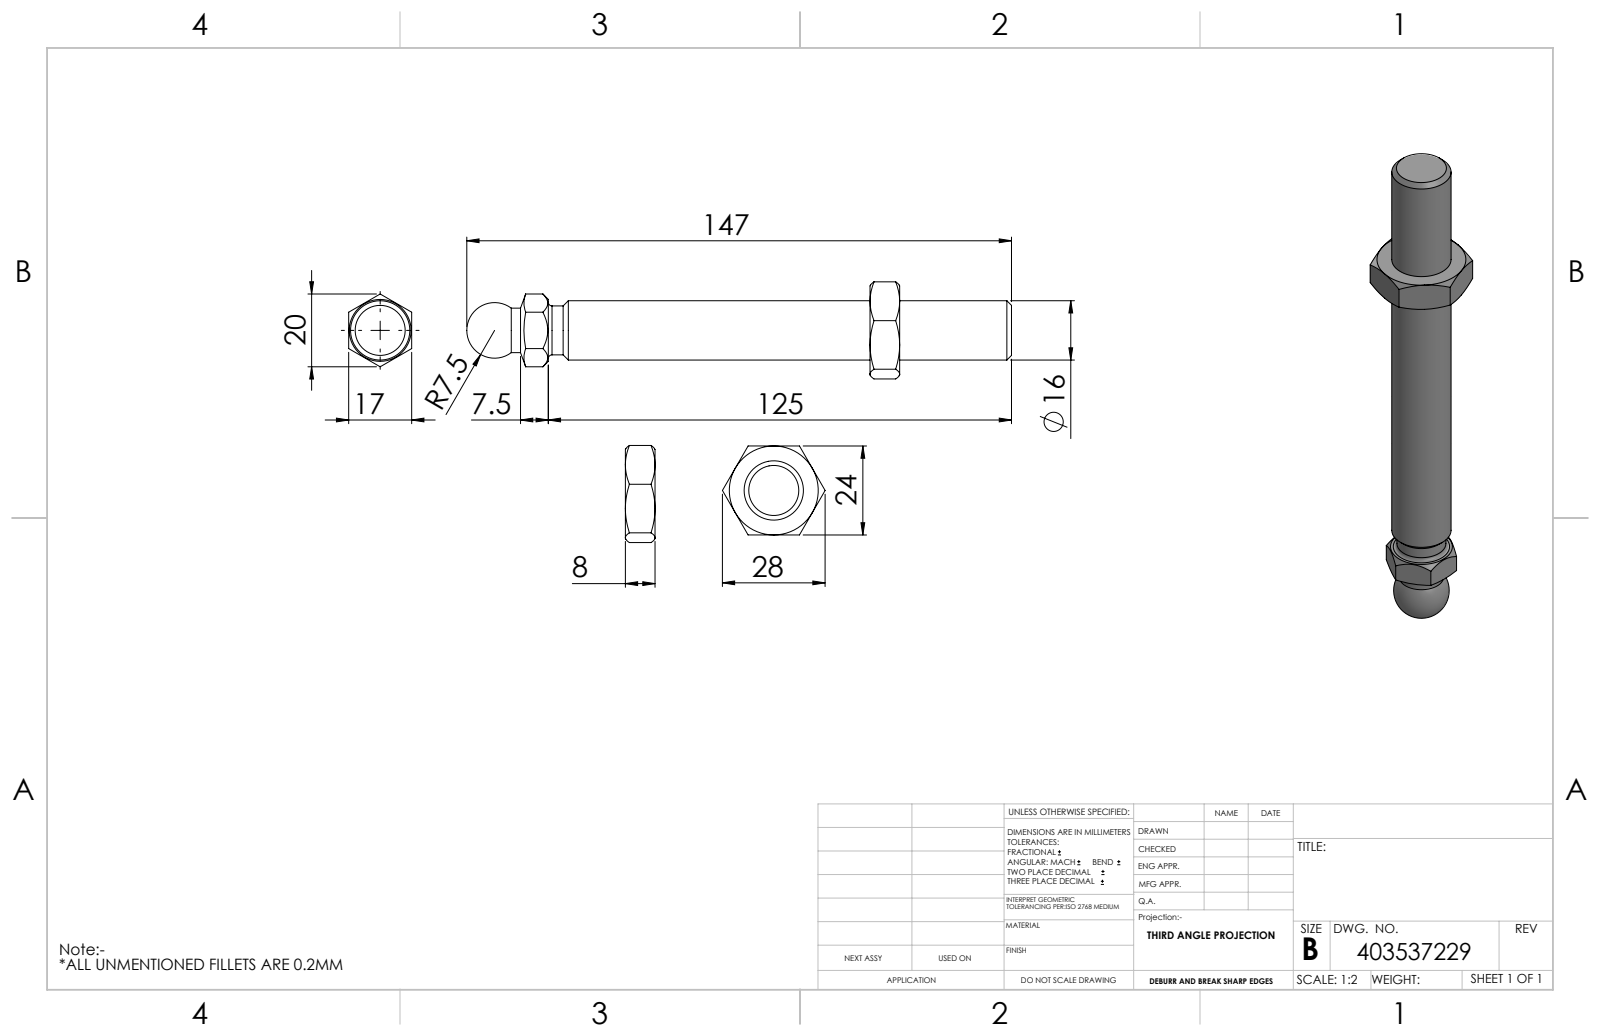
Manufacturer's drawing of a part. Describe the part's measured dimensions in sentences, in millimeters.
The part is named "403537229". Its 3-D file was written by "SolidWorks 2014 (AUTOMOTIVE_DESIGN)". It is 2 solids with 56 faces: 16 planar, 10 cylindrical and 30 other. Overall it measures 147 by 27.21 by 26.19 millimeters. Its volume is 31 149 cubic millimeters and its surface area 9 307 square millimeters. Round holes: 1 of diameter 14, 1 of diameter 16. Round bosses or shafts: 1 of diameter 13.2, 1 of diameter 12. The main face-to-face distances are 8, 24, 17, 38.18, 30.18, 24.01, 86.82, 94.82, 125.
